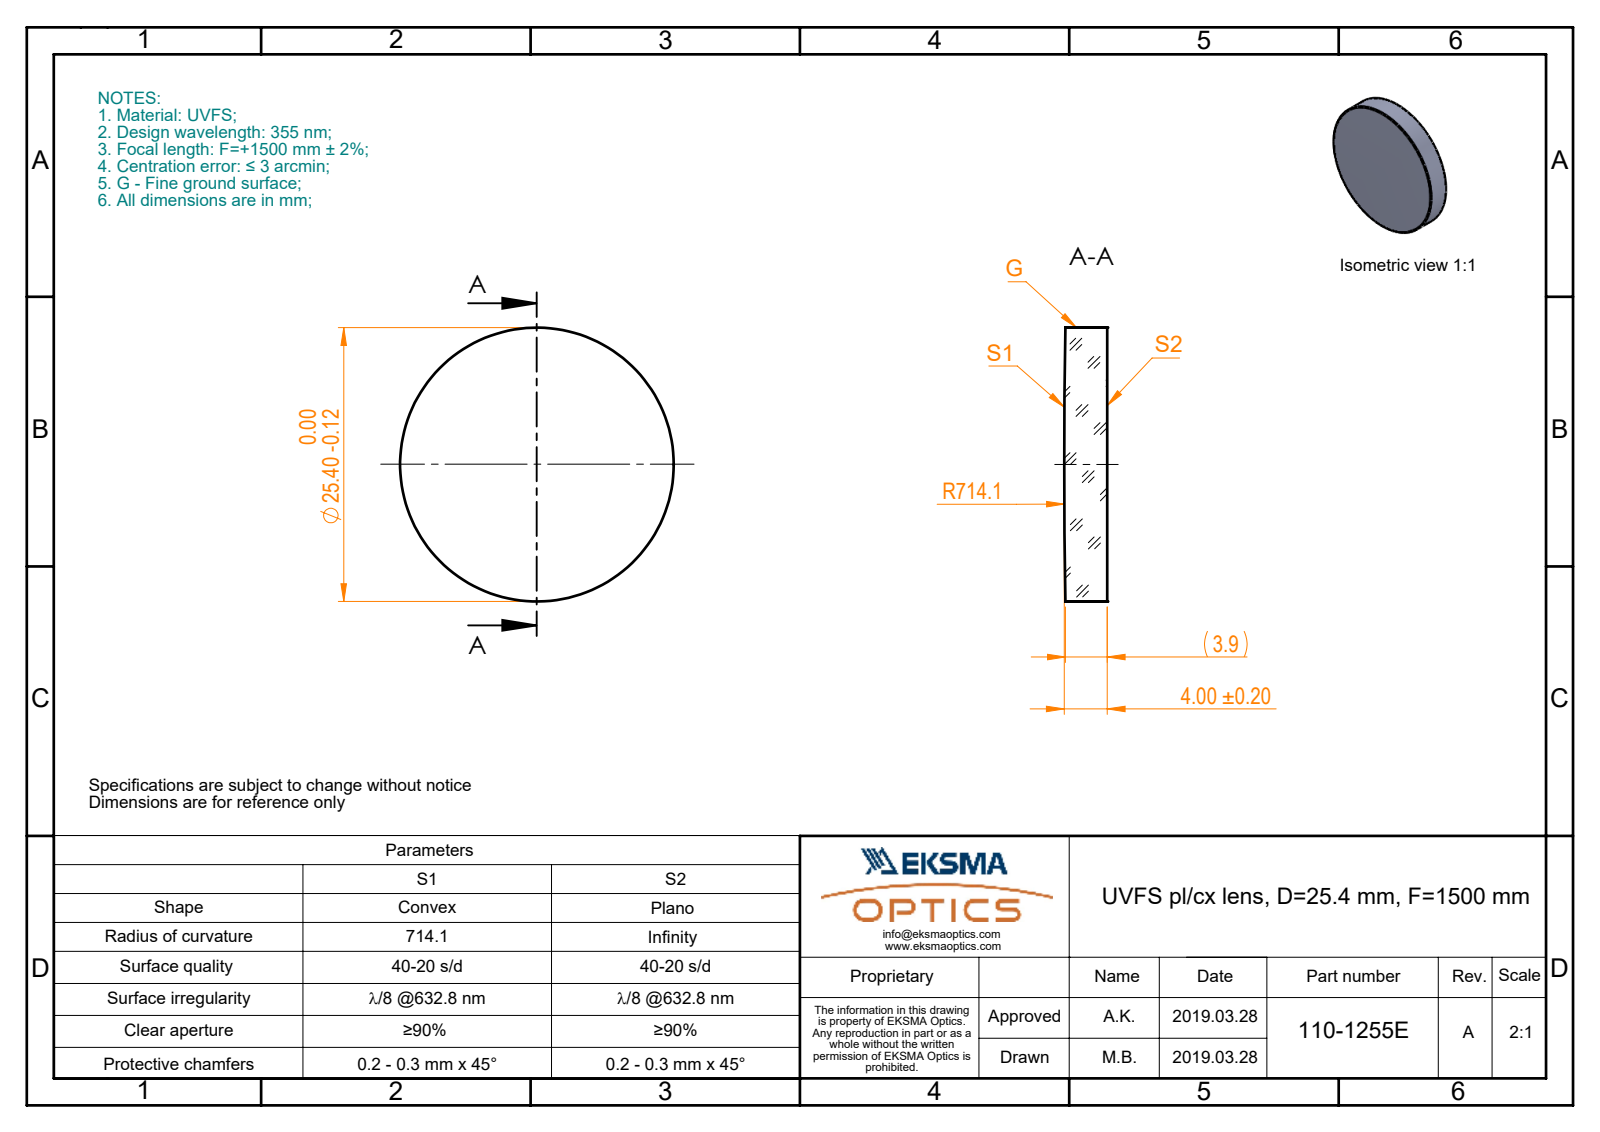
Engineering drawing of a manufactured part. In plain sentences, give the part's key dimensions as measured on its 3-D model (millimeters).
The part is named "110-1255E UVFS pl-cx 25.4 F1500". Its 3-D file was written by "SolidWorks 2017 (CONFIG_CONTROL_DESIGN)". It is 1 solid with 5 faces: 1 planar, 2 cylindrical and 2 other. Overall it measures 25.4 by 25.4 by 4 millimeters. Its volume is 1 998 cubic millimeters and its surface area 1 324 square millimeters. Round bosses or shafts: 1 of diameter 25.4.
